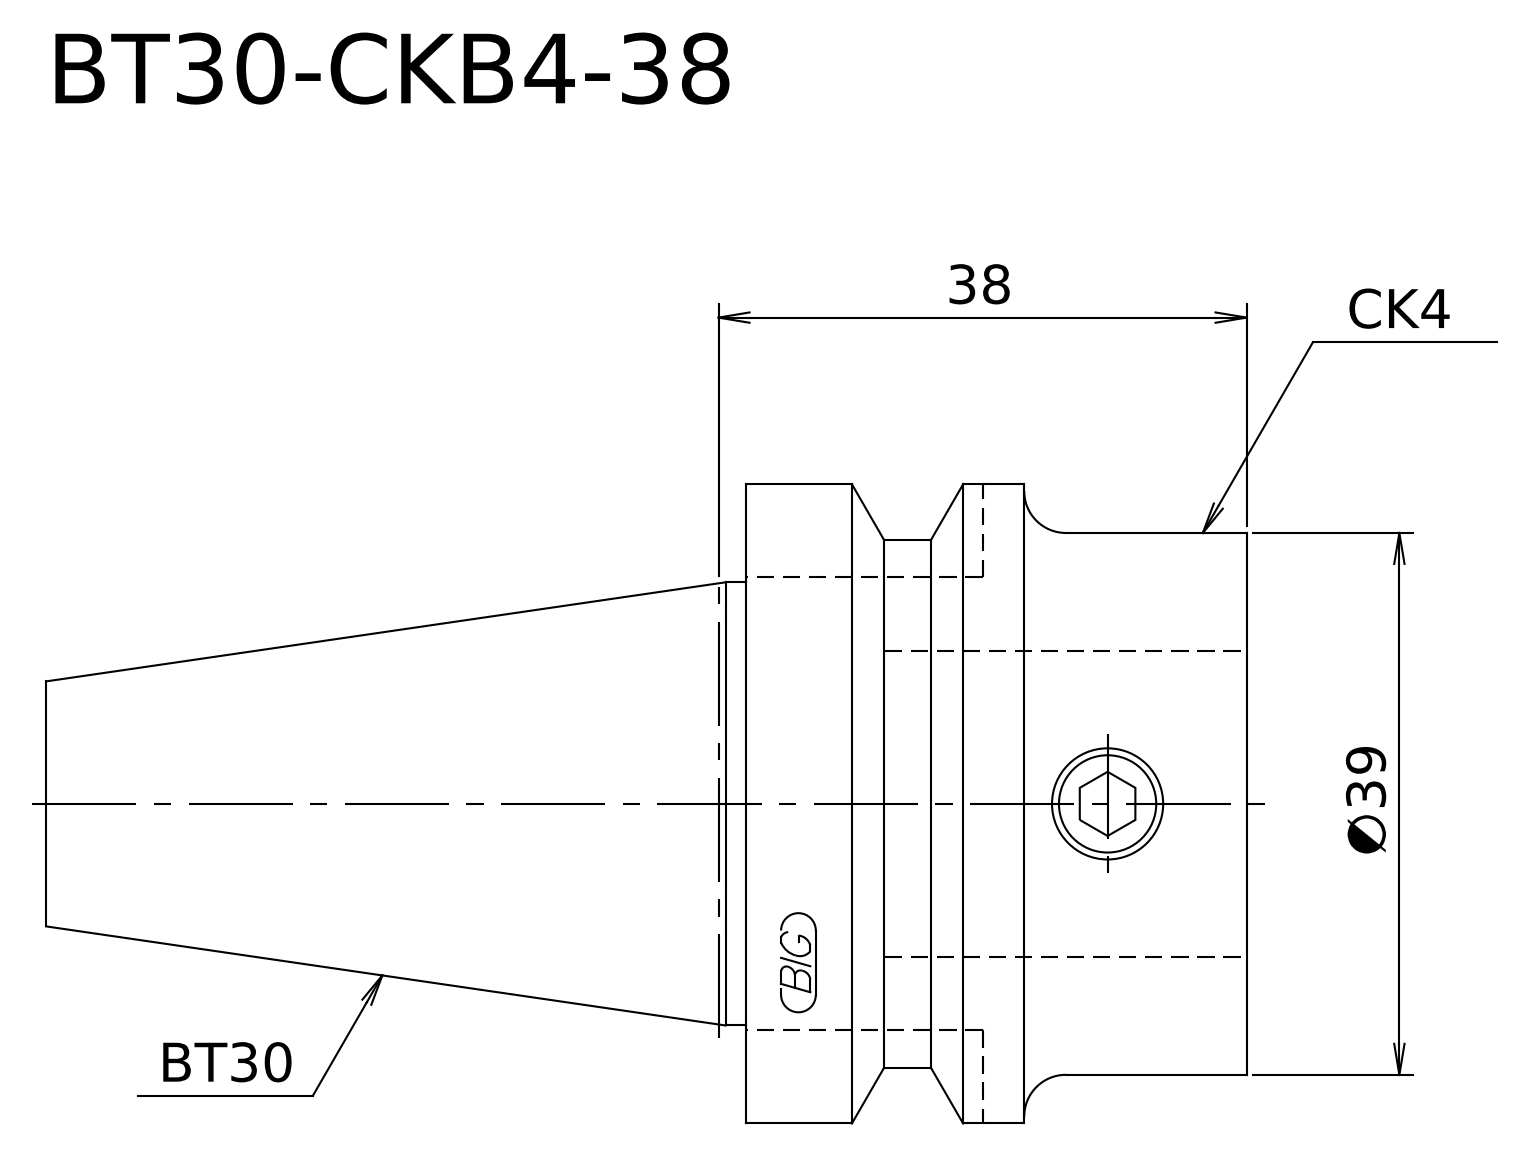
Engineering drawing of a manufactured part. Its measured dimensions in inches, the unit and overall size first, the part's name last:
Units: inches
Overall size (bounding box): 3.402 × 1.811 × 1.811
Round bosses / shafts (diameter × count): ⌀1.811 ×1, ⌀1.535 ×1, ⌀1.496 ×1, ⌀1.256 ×1
Main face-to-face distances: 1.417, 3.402, 1.984, 0.63, 0.787, 2.772
Volume: 4.591 in³ · Surface area: 18.43 in²
Bodies: 1 solid, 13 faces (4 planar, 5 cylindrical, 4 other)
STEP written by: Kubotek KeyCreator V8.5.1 (14335) (CONFIG_CONTROL_DESIGN)
